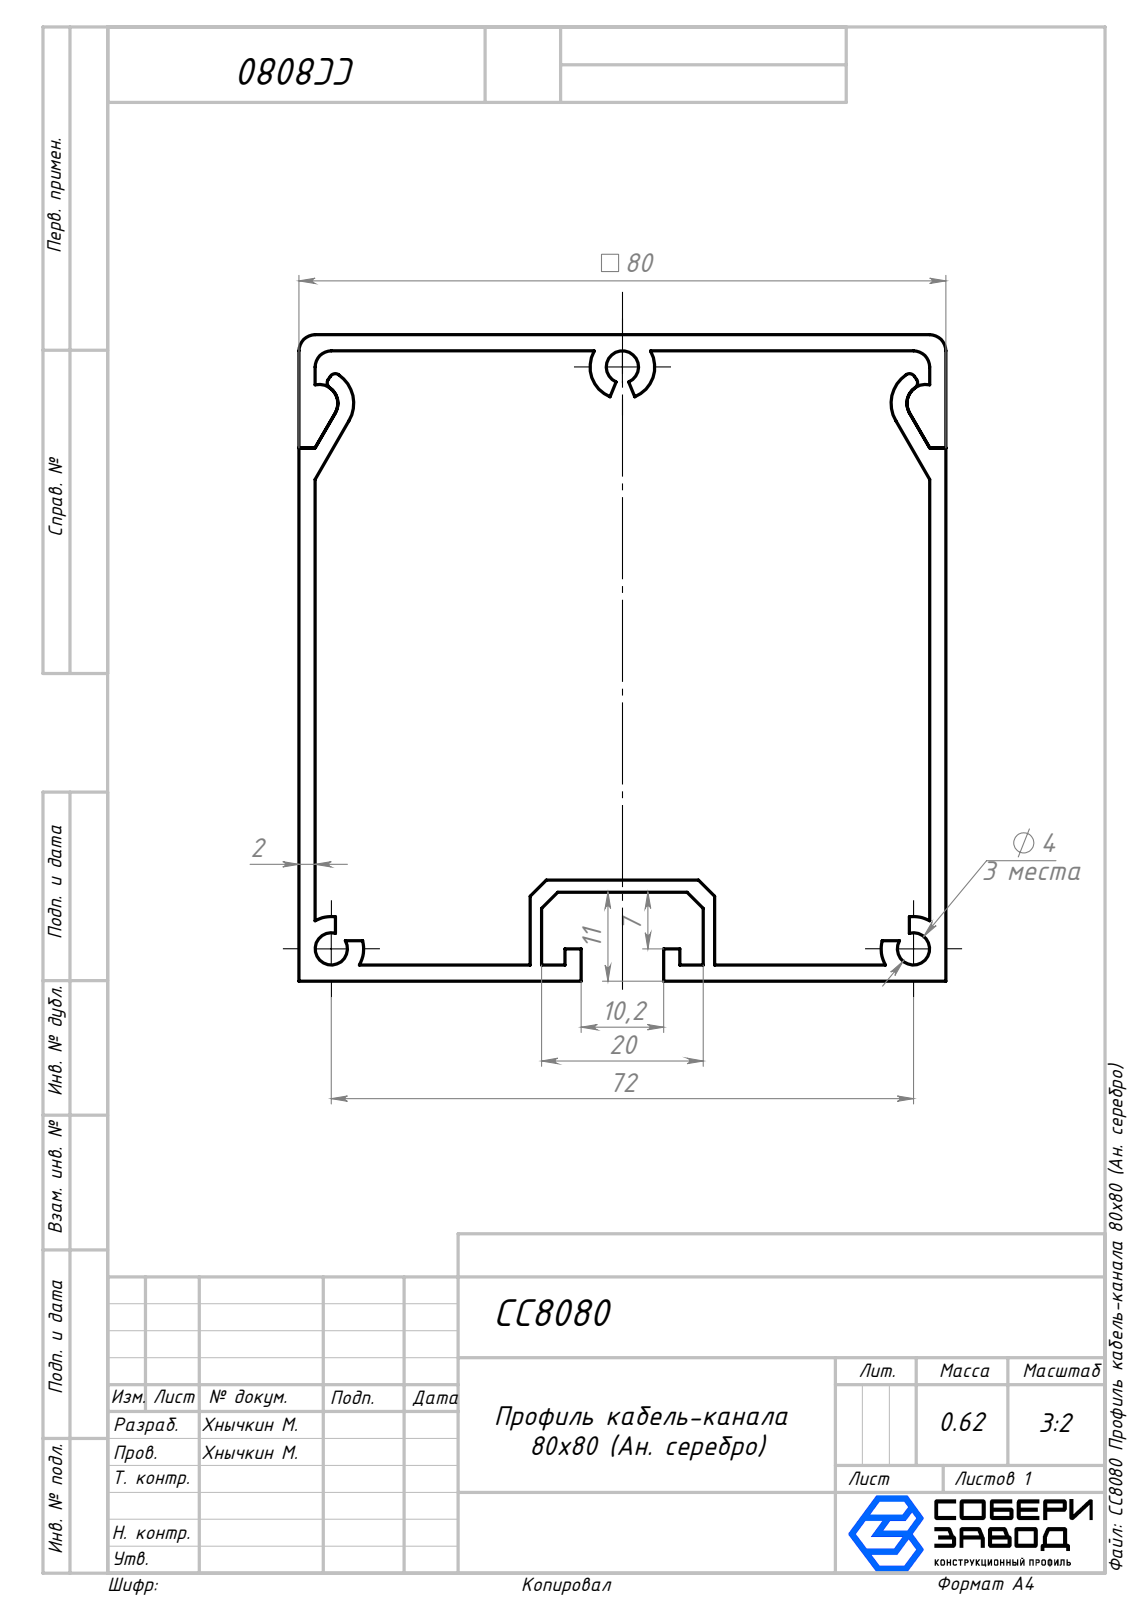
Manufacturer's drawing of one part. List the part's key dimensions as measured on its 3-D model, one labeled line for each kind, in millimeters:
Part name (STEP PRODUCT): CC8080 Профиль кабель-канала 80х80 (Ан. серебро); Алюм. кабель 80х80_00; Алюм. кабель, крышка 80х80_00
STEP written by: SolidWorks 2026 (AUTOMOTIVE_DESIGN)
Units: millimetres
Bodies: 2 solids, 92 faces (57 planar, 35 cylindrical, 0 other)
Overall size (bounding box): 100 × 80 × 80
Volume: 79 603 mm³ · Surface area: 80 143 mm²
Round holes (diameter × count): ⌀4 ×3
Partial cylindrical surfaces — rounded edges, fillets, slot ends (radius × count): R0.75 ×4, R2 ×4, R4 ×3, R2.35 ×2, R4.3 ×2
Main face-to-face distances: 2, 78, 80, 76, 12.5, 10.5, 65.5, 67.5, 28.6, 51.4
Hole centre spacings: 80.5, 72
